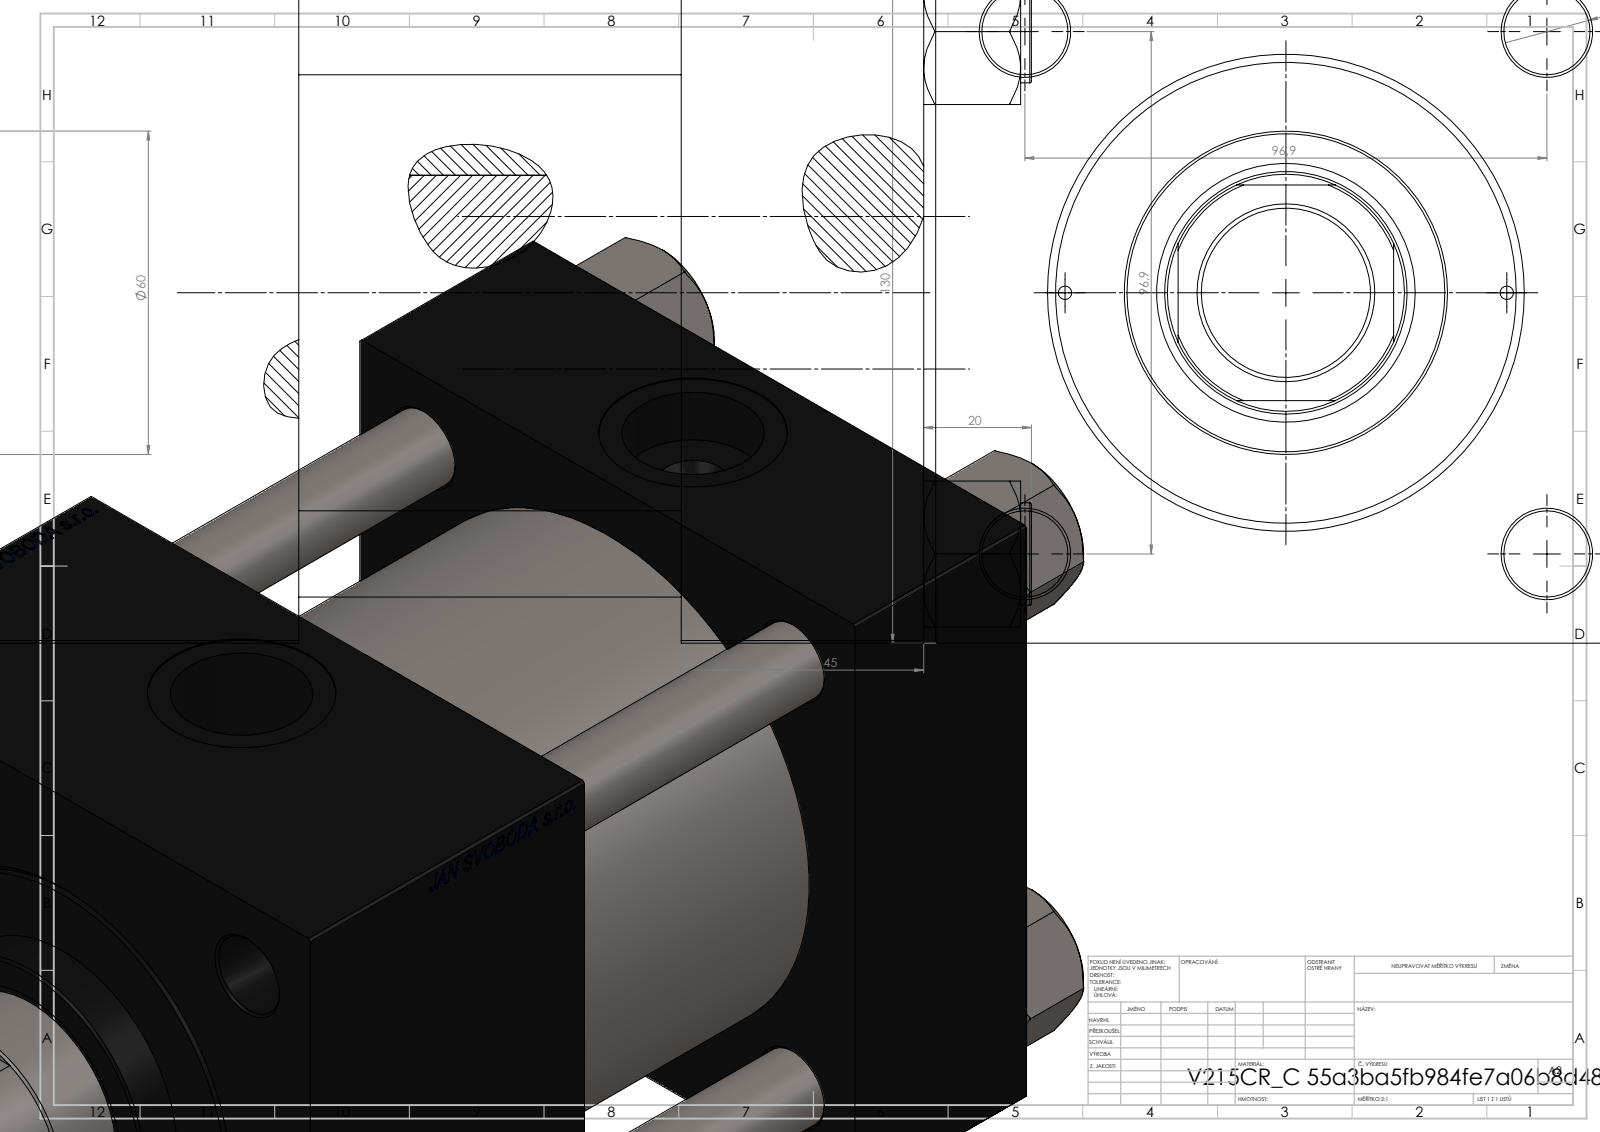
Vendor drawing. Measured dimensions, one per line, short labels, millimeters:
name: NUT_M5_C; V215CR_VCP_C; V215_VC_A; V215CR_C_TYCINKA (+2 more)
written by: SolidWorks 2019 (CONFIG_CONTROL_DESIGN)
unit: mm
bodies: 12 solids, 1217 faces (580 planar, 95 cylindrical, 542 other)
size: 288 × 130 × 130
volume: 2 463 000 mm³; area: 332 938 mm²
holes: 4× ⌀16, 2× ⌀2.5, 2× ⌀7, 2× ⌀26.44, 2× ⌀35, 1× ⌀31.5, 1× ⌀45, 1× ⌀48, 1× ⌀76, 1× ⌀85.5, 1× ⌀100
bosses: 4× ⌀19, 1× ⌀106, 1× ⌀60, 1× ⌀33, 1× ⌀31
rounds: 1× R22
face distances: 130, 45, 188, 143, 116, 71, 72, 20, 96, 51
hole spacings: 49.02, 68.52, 96.9, 101.73, 41, 137.04, 82, 118.5
